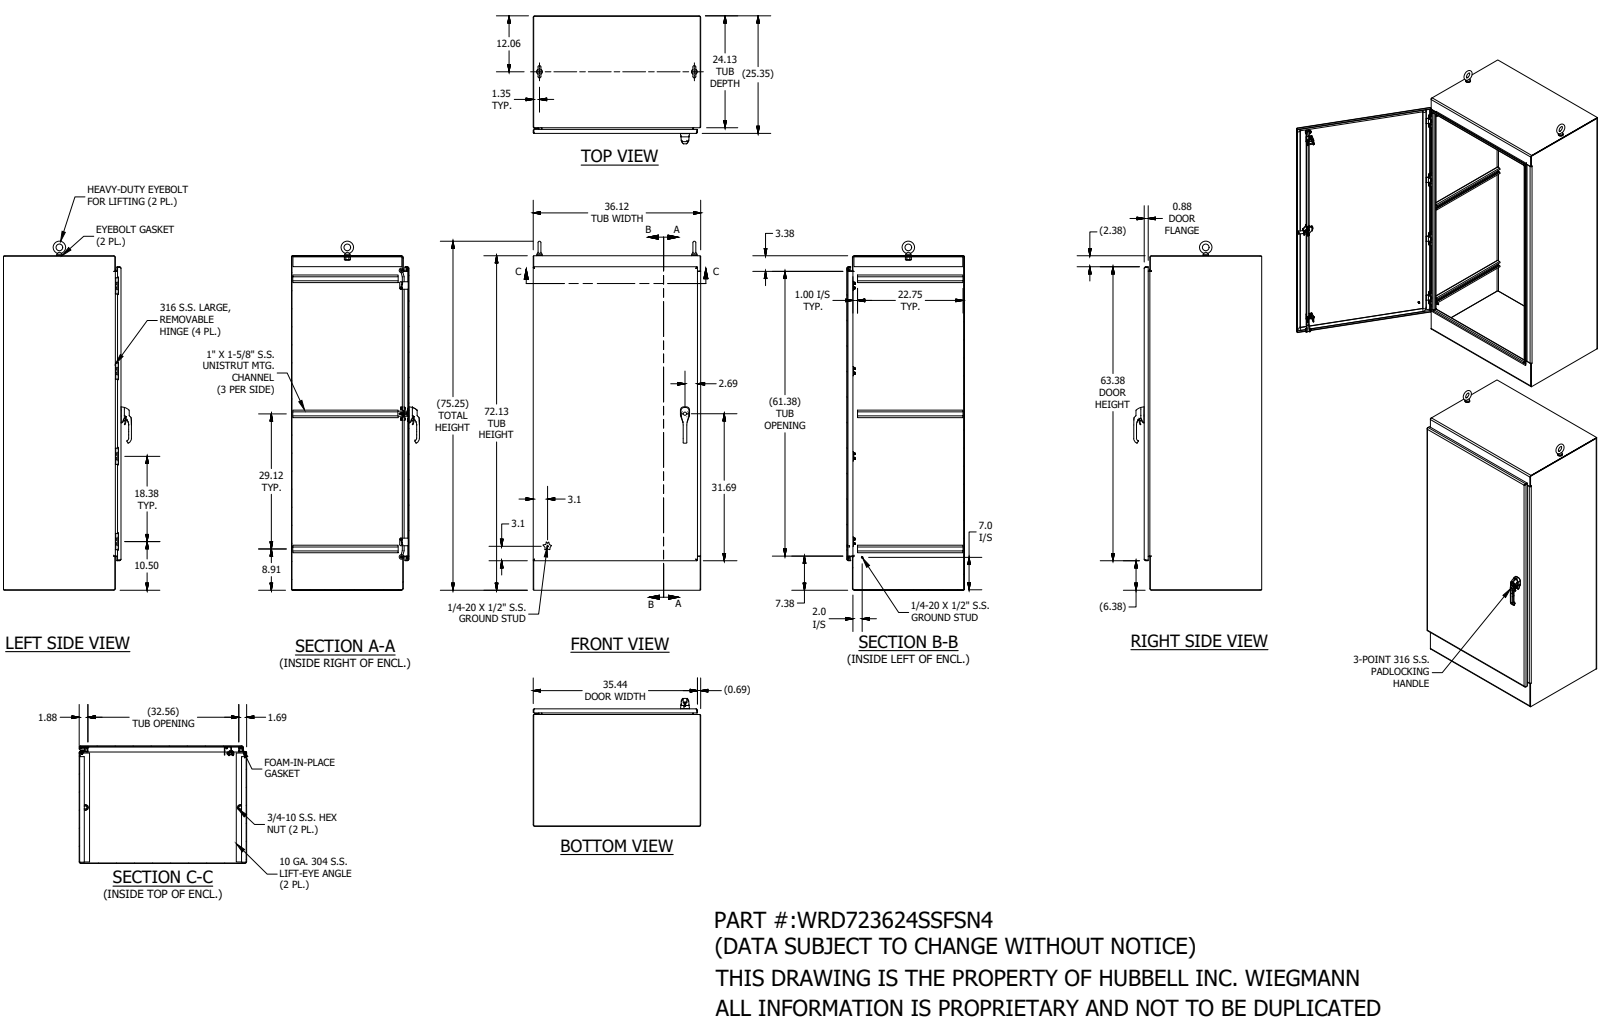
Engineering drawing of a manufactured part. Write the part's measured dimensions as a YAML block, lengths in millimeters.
part_name: "WRD723624SSFSN4"
step_written_by: "SolidWorks 2019 (AUTOMOTIVE_DESIGN)"
units: millimeters
bodies: {solids: 103, faces: 3881, planar: 1580, cylindrical: 1362, other: 939}
overall_size: [1911.3, 917.7, 701]
volume: 21470000
surface_area: 15800000
round_holes:
  - {diameter: 3.6, count: 24}
  - {diameter: 5, count: 8}
  - {diameter: 6.7, count: 8}
  - {diameter: 6.8, count: 8}
  - {diameter: 7.5, count: 8}
  - {diameter: 16.5, count: 8}
  - {diameter: 3.5, count: 4}
  - {diameter: 4.2, count: 4}
  - {diameter: 4.7, count: 4}
  - {diameter: 5.1, count: 4}
  - {diameter: 5.4, count: 3}
  - {diameter: 7.1, count: 3}
round_bosses_or_shafts:
  - {diameter: 15.9, count: 8}
  - {diameter: 6.4, count: 7}
  - {diameter: 6, count: 4}
  - {diameter: 6, count: 3}
  - {diameter: 31.8, count: 2}
  - {diameter: 28.4, count: 2}
  - {diameter: 25.4, count: 2}
  - {diameter: 19.1, count: 2}
partial_cylinders:
  - {radius: 0.5, count: 172}
  - {radius: 0.3, count: 114}
  - {radius: 3.2, count: 34}
  - {radius: 0.5, count: 21}
  - {radius: 1.6, count: 18}
  - {radius: 1.3, count: 14}
  - {radius: 1.6, count: 14}
  - {radius: 2, count: 14}
face_to_face_distances: [2.6, 914.9, 641.2, 638.6, 643.9, 641.2, 2.6, 912.3, 1829.3, 917.6]
hole_center_spacings: [0.5, 0.6, 0.6, 9.7, 19.3, 25.4, 466.7, 933.5]
